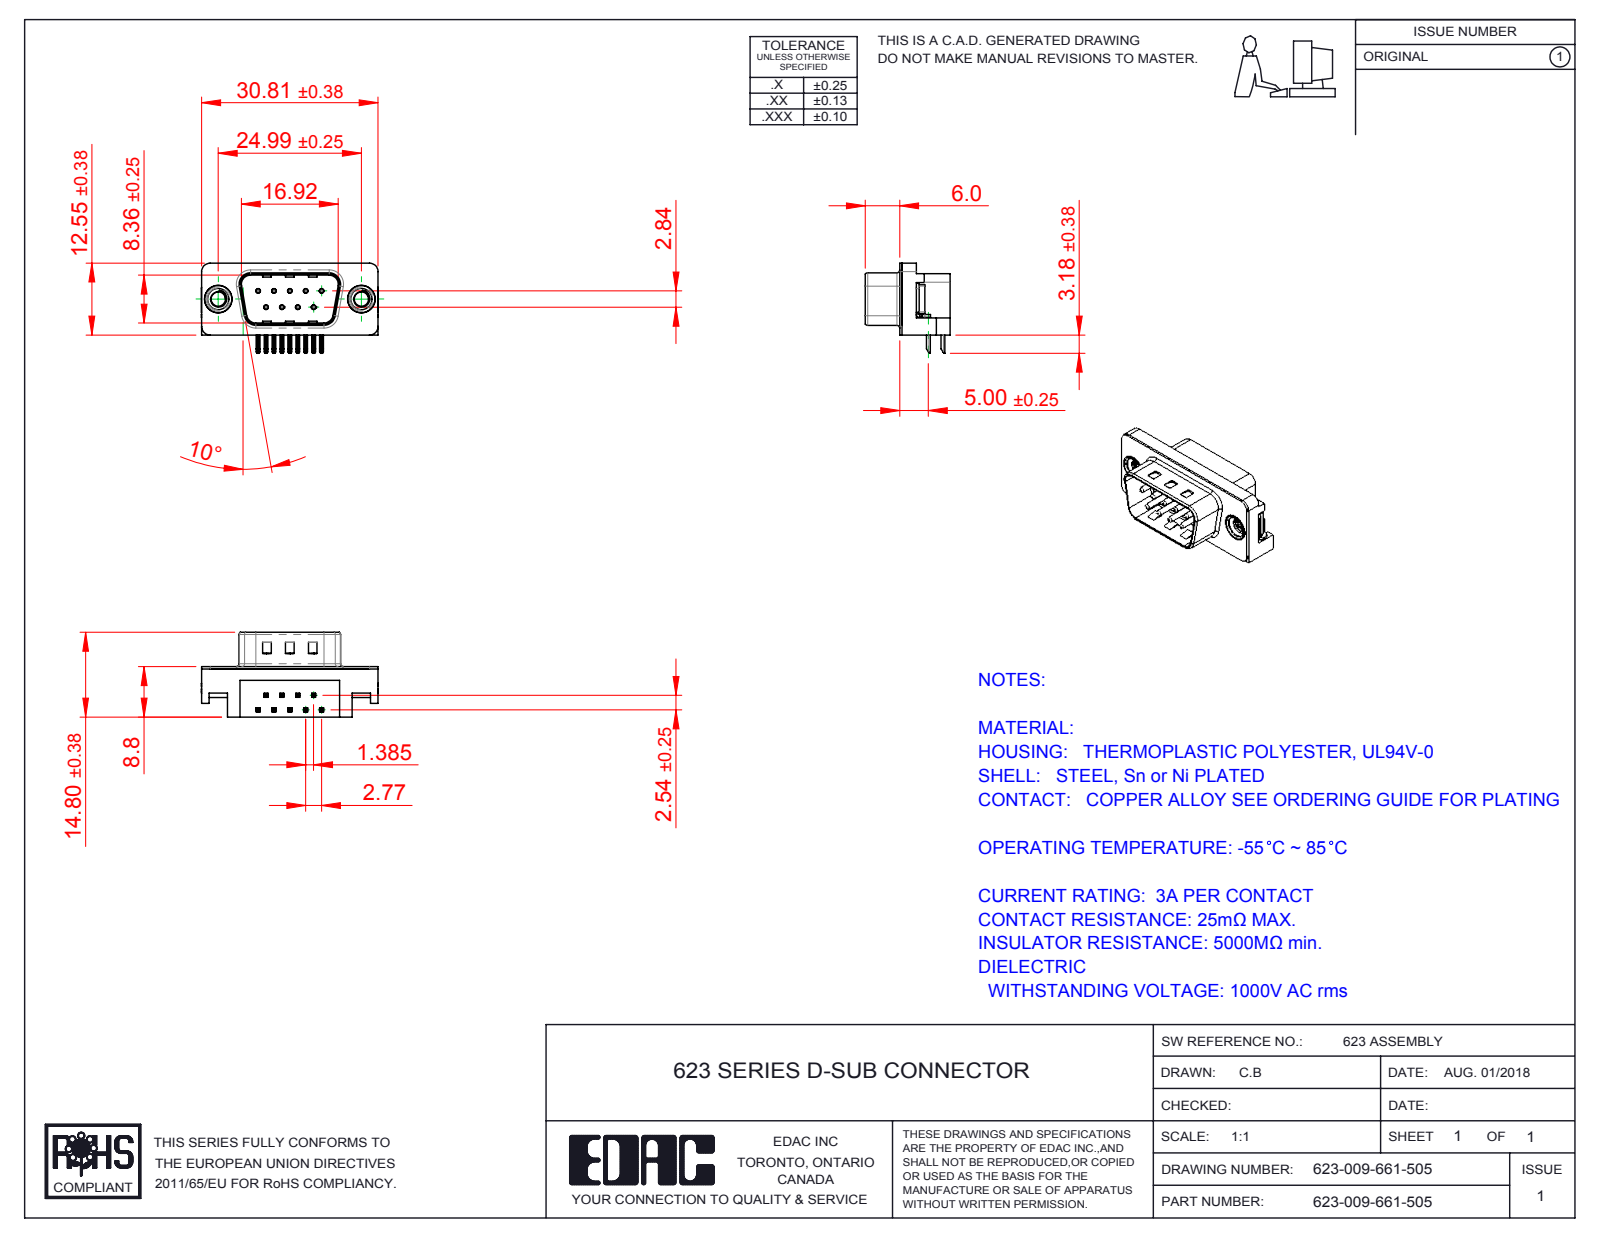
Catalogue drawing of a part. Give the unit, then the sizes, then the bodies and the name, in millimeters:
Units: millimetres
Overall size (bounding box): 30.89 × 15.73 × 14.8
Round holes (diameter × count): ⌀0.35 ×9, ⌀0.8 ×9, ⌀2.5 ×2, ⌀4 ×2, ⌀4.8 ×2, ⌀5 ×2
Round bosses / shafts (diameter × count): ⌀0.75 ×9, ⌀4.9 ×2, ⌀4.75 ×2, ⌀3.9 ×2
Partial cylindrical surfaces — rounded edges, fillets, slot ends (radius × count): R0.25 ×44, R0.12 ×18, R1 ×16, R0.5 ×9, R1.5 ×8, R0.9 ×4, R1.6 ×4, R2 ×4
Main face-to-face distances: 0.4, 8.4, 8.8, 5.9, 2.9, 2.5, 0.35, 8.76, 10.69, 10.34
Hole centre spacings: 3.16, 2.77, 5.54, 5.03, 5.04, 8.31, 7.48, 7.49
Volume: 2 462 mm³ · Surface area: 3 779 mm²
Bodies: 15 solids, 981 faces (573 planar, 309 cylindrical, 99 other)
Part name (STEP PRODUCT): 623 M3 Threaded Rivet; 623 Contact Bottom; 623 Shell_9 Socket; 623 Contact Top (+3 more)
STEP written by: SolidWorks 2016 (CONFIG_CONTROL_DESIGN)
